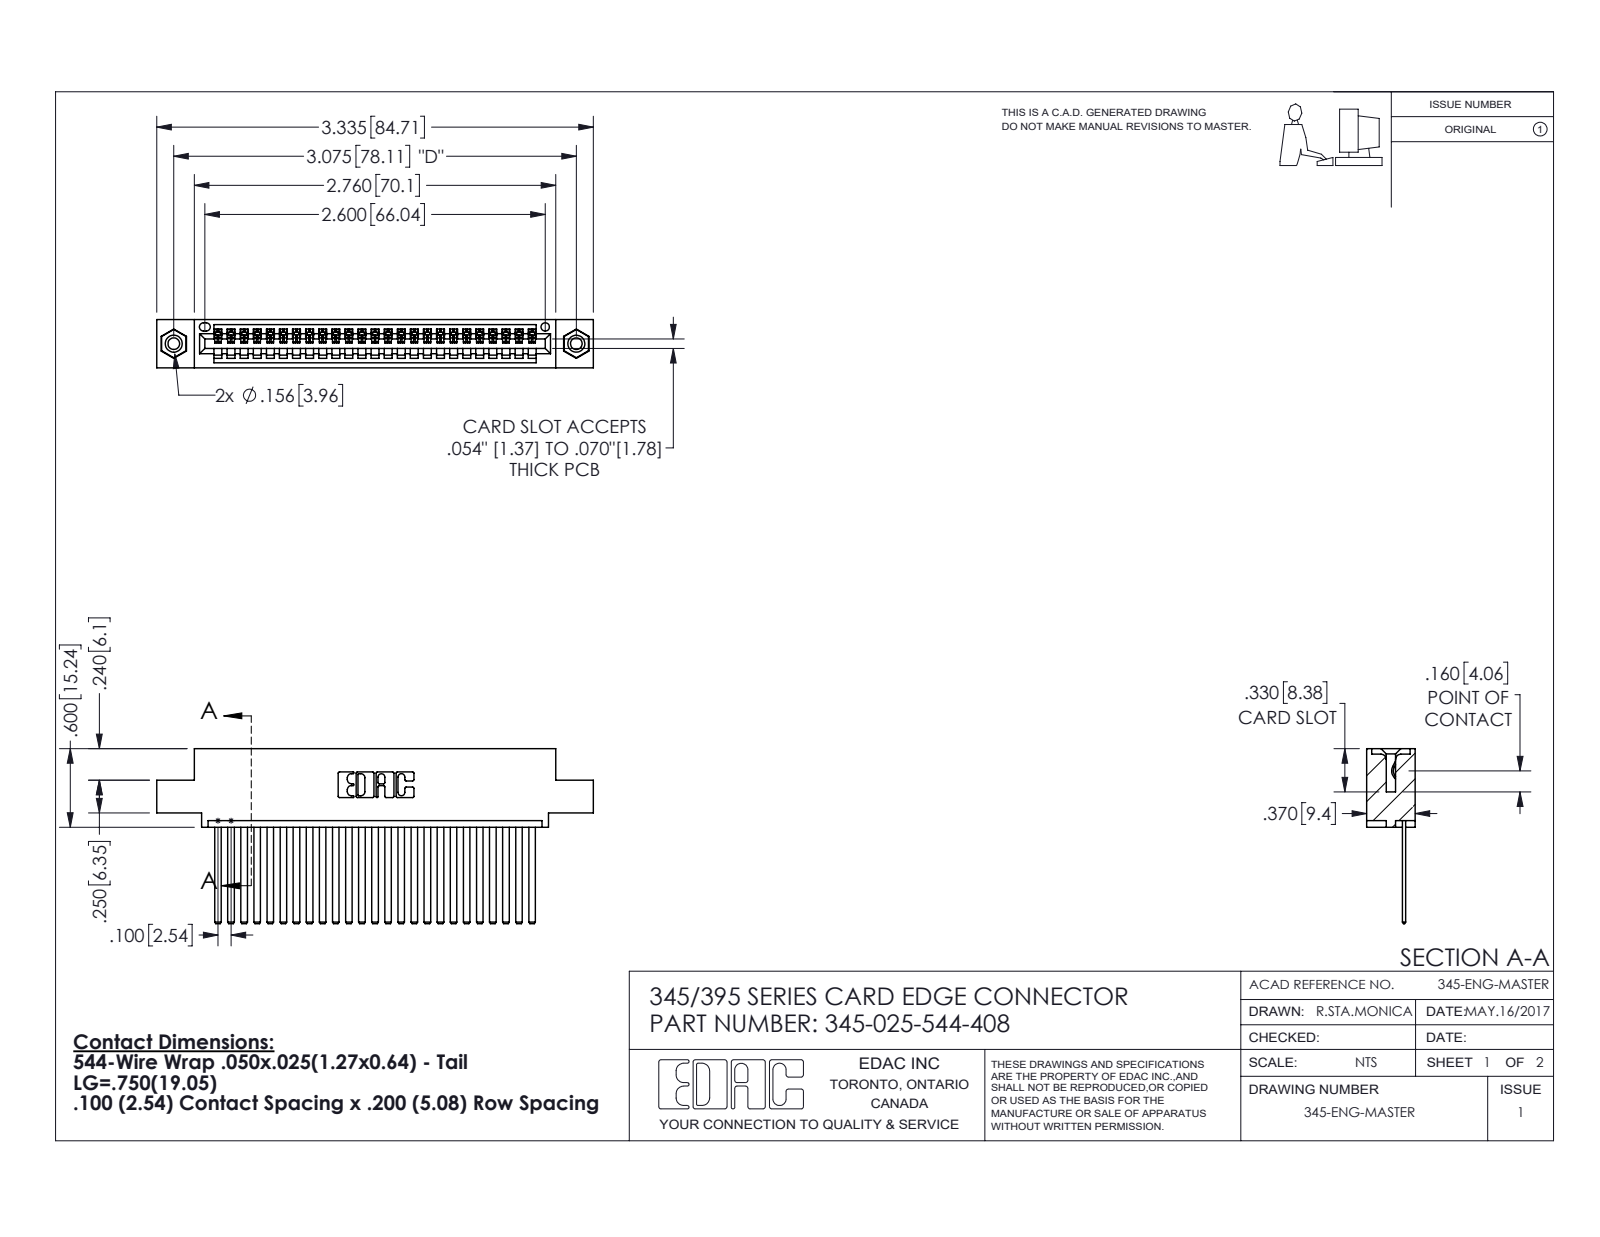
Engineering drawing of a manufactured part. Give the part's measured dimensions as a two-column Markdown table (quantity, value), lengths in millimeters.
| quantity | value |
| --- | --- |
| part name | 345-025-544-408; 345 Part_0.110 Offset - 0.156 Dia-TI; 345-292-001_345-293-144; 345-250-001_345-250-003-102 |
| STEP written by | SolidWorks 2016 (CONFIG_CONTROL_DESIGN) |
| units | millimeters |
| bodies | 28 solids, 1490 faces (1016 planar, 458 cylindrical, 16 other) |
| overall size | 84.7 × 34 × 9.4 |
| volume | 8 110 mm³ |
| surface area | 11 520 mm² |
| round holes (diameter × count) | 2.3 × 2, 3.2 × 2, 4 × 2, 1.6 × 1 |
| round bosses / shafts (diameter × count) | 3.9 × 2 |
| partial cylindrical surfaces (radius × count) | 0.2 × 50, 0.3 × 22, 0.2 × 6, 0.8 × 6, 0.7 × 3, 0.8 × 2, 1 × 2, 0.4 × 1 |
| main face-to-face distances | 1.8, 7.6, 2.5, 0.6, 6.9, 9.4, 5.1, 5.7, 3.8, 1.8 |
| hole center spacings | 6.9, 72.1, 78.1 |
